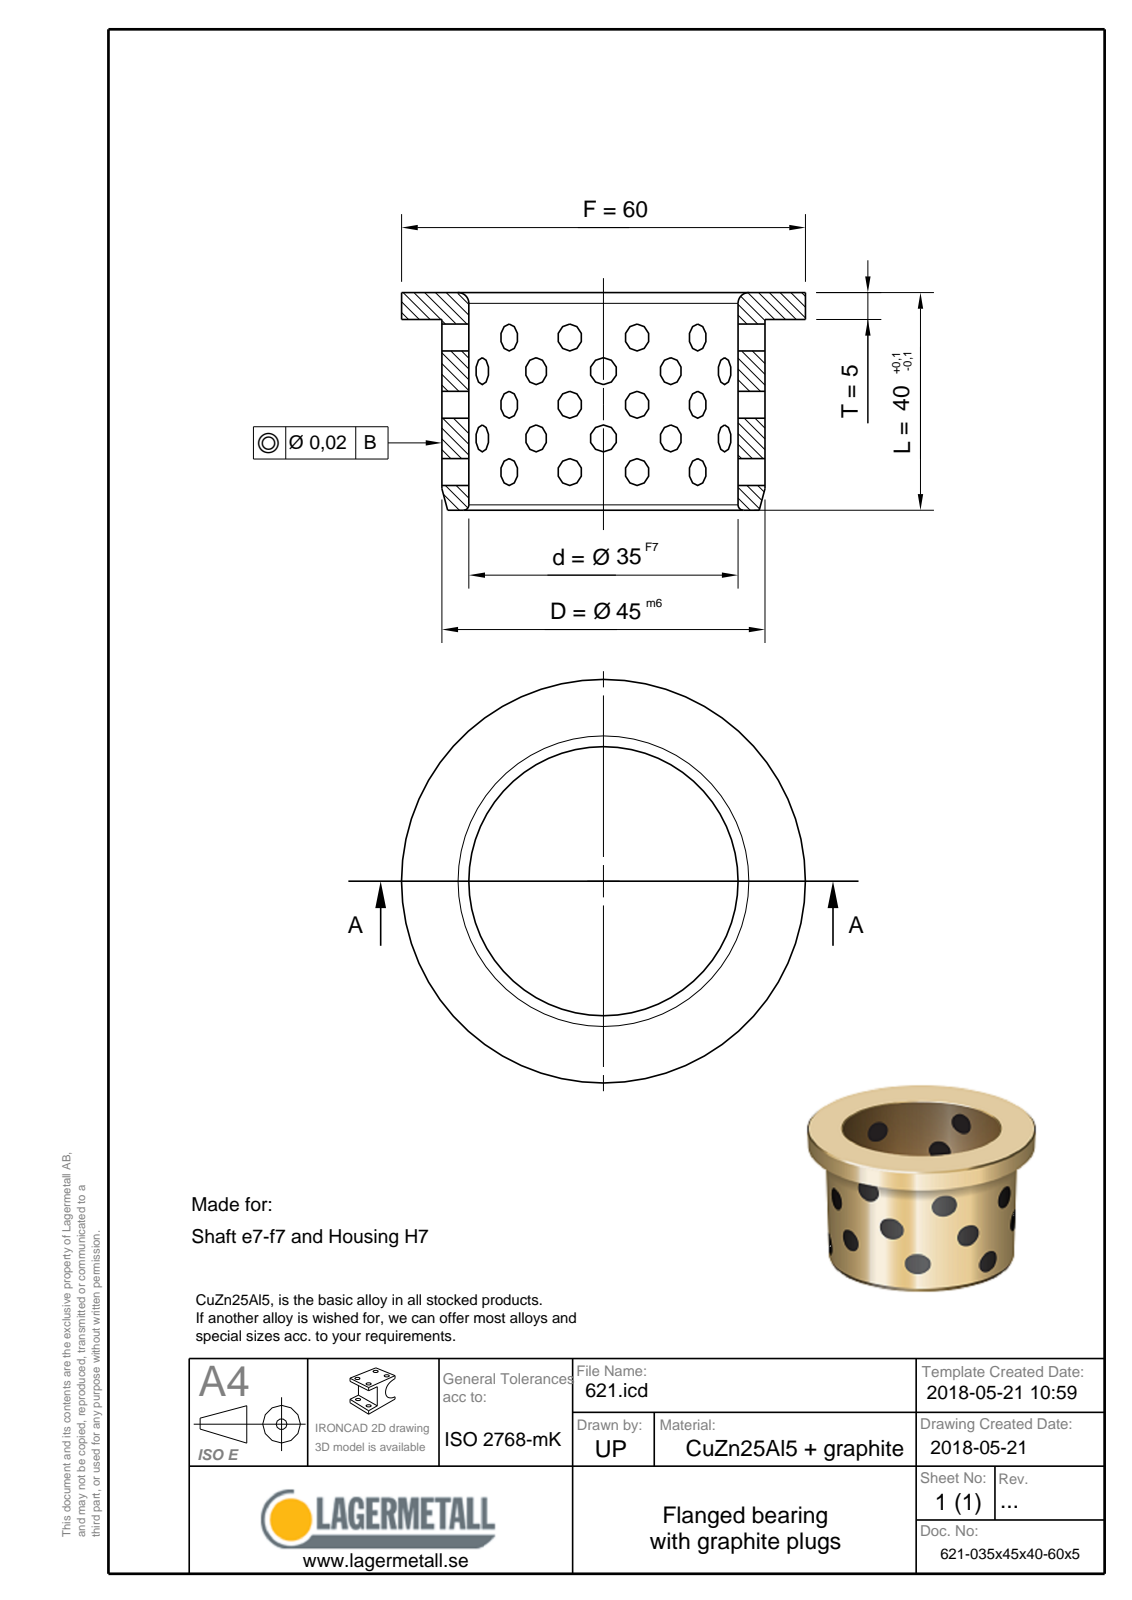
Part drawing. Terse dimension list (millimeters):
name: 621-035x45x40-60x5
written by: Spatial InterOp 3D (CONFIG_CONTROL_DESIGN)
unit: mm
bodies: 1 solid, 9 faces (3 planar, 3 cylindrical, 3 other)
size: 60 × 60 × 40
volume: 30 953 mm³; area: 13 725 mm²
holes: 1× ⌀35
bosses: 1× ⌀60, 1× ⌀45
face distances: 5, 35, 40
